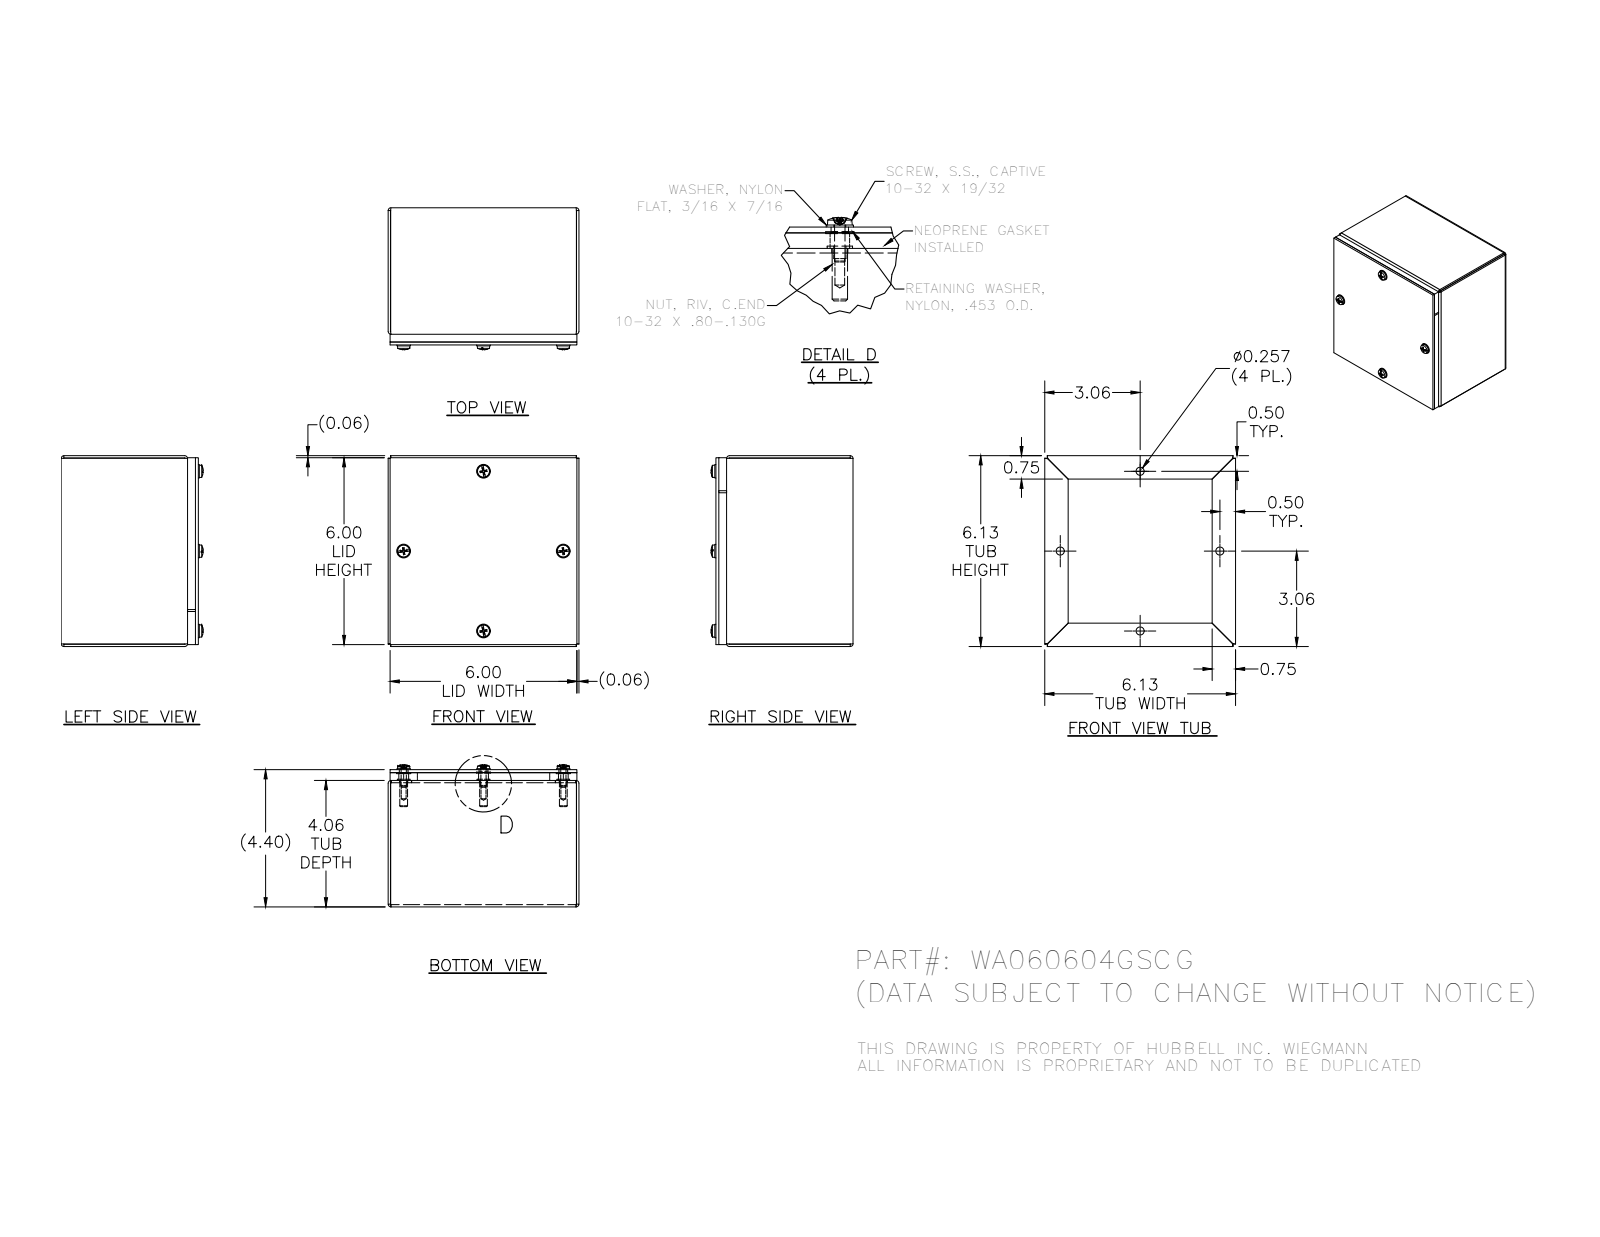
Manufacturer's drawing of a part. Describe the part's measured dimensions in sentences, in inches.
The part is named "34984; WA0606GSCGLP; 37210; WA060604GSCG (+4 more)". Its 3-D file was written by "SolidWorks 2014 (AUTOMOTIVE_DESIGN)". It is 20 solids with 496 faces: 244 planar, 128 cylindrical and 124 other. Overall it measures 6.125 by 6.125 by 4.558 inches. Its volume is 18.81 cubic inches and its surface area 428.3 square inches. Round holes: 4 of diameter 0.156, 4 of diameter 0.188, 4 of diameter 0.196, 4 of diameter 0.257, 4 of diameter 0.278, 4 of diameter 0.281, 4 of diameter 0.313. Round bosses or shafts: 4 of diameter 0.453, 4 of diameter 0.437, 4 of diameter 0.406, 4 of diameter 0.248, 4 of diameter 0.167. Partial cylindrical surfaces (rounded edges, fillets, slot ends): 8 of radius 0.016, 8 of radius 0.09, 4 of radius 0.089. The main face-to-face distances are 0.074, 6.051, 6.125, 5.977, 3.986, 0.094, 4.33, 4.404, 4.31, 4.236. The hole center spacings are 3.624, 3.623, 3.623, 5.124, 5.125, 3.624, 3.625, 5.124.
